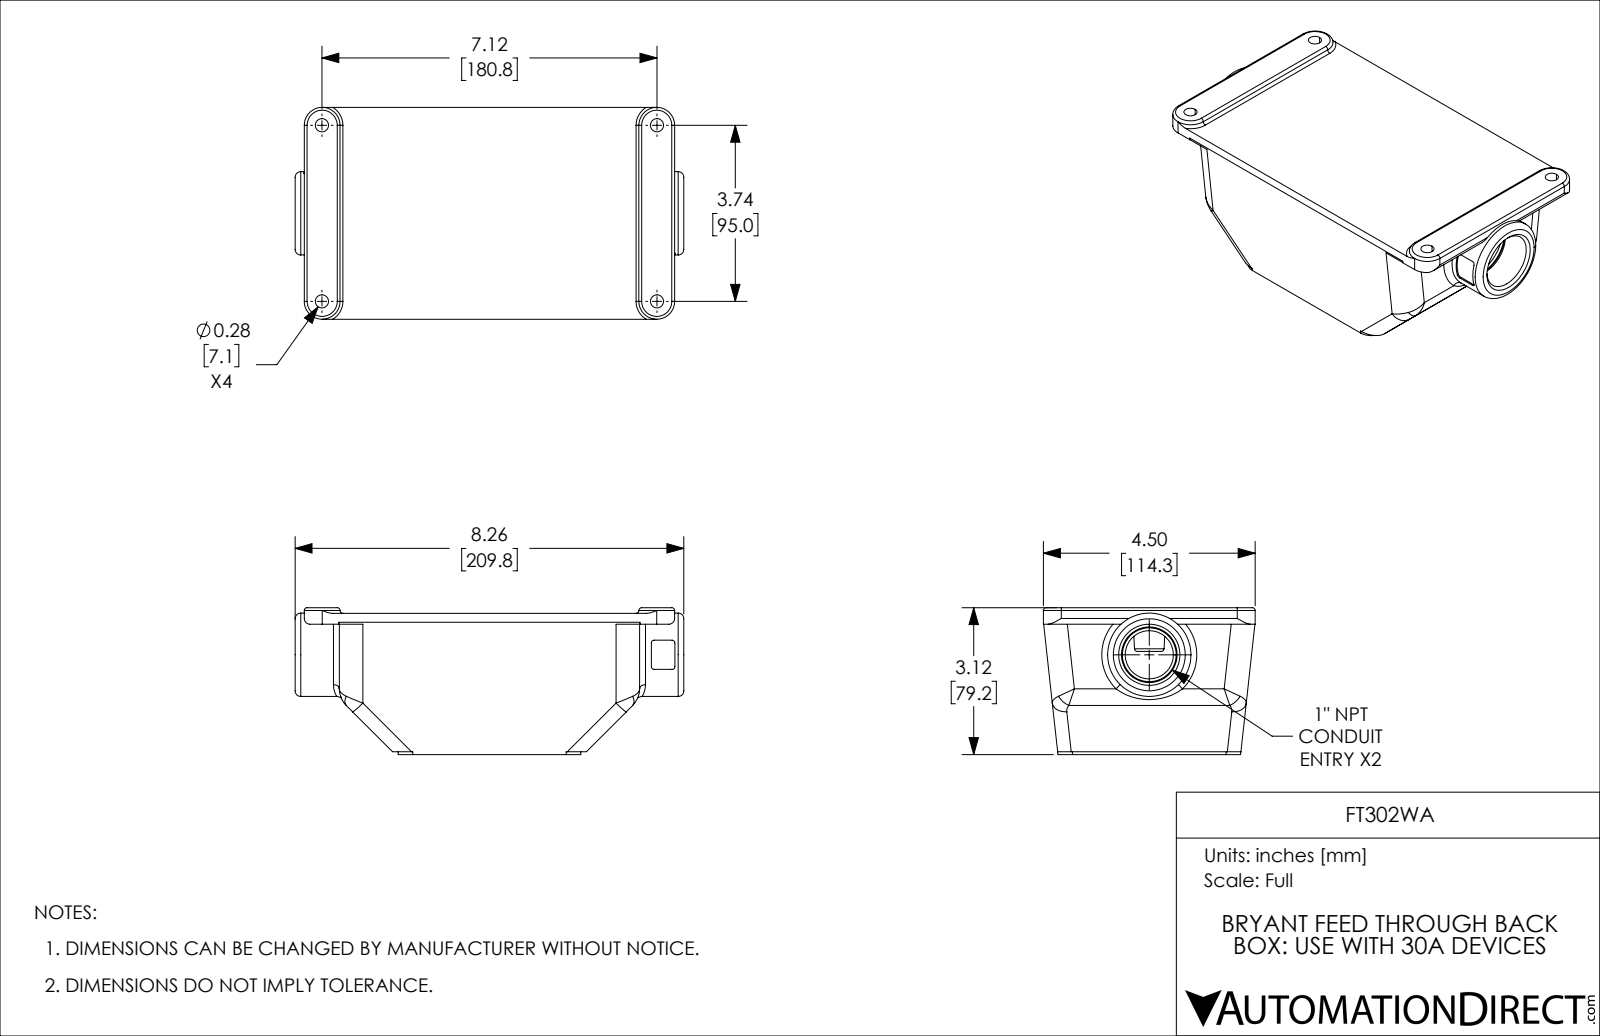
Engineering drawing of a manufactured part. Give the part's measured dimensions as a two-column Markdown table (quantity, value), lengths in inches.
| quantity | value |
| --- | --- |
| part name | FT302WA |
| STEP written by | SolidWorks 2021 (CONFIG_CONTROL_DESIGN) |
| units | inches |
| bodies | 1 solid, 432 faces (82 planar, 228 cylindrical, 122 other) |
| overall size | 8.26 × 4.5 × 3.12 |
| volume | 22.05 in³ |
| surface area | 210.9 in² |
| round holes (diameter × count) | 0.145 × 4, 0.28 × 4, 0.13 × 1, 1.023 × 1, 1.18 × 1, 1.38 × 1 |
| round bosses / shafts (diameter × count) | 1.77 × 1 |
| partial cylindrical surfaces (radius × count) | 0.06 × 38, 0.09 × 12, 0.12 × 10, 0.31 × 10, 0.5 × 6, 0.19 × 4, 0.254 × 4, 0.38 × 4 |
| main face-to-face distances | 0.19, 0.19, 3, 2.81, 0.12, 0.31, 3.12, 6.19, 6, 0.35 |
| hole center spacings | 2.021, 3.125, 3.971, 5.131, 6.166, 1.651, 3.027, 3.146 |
